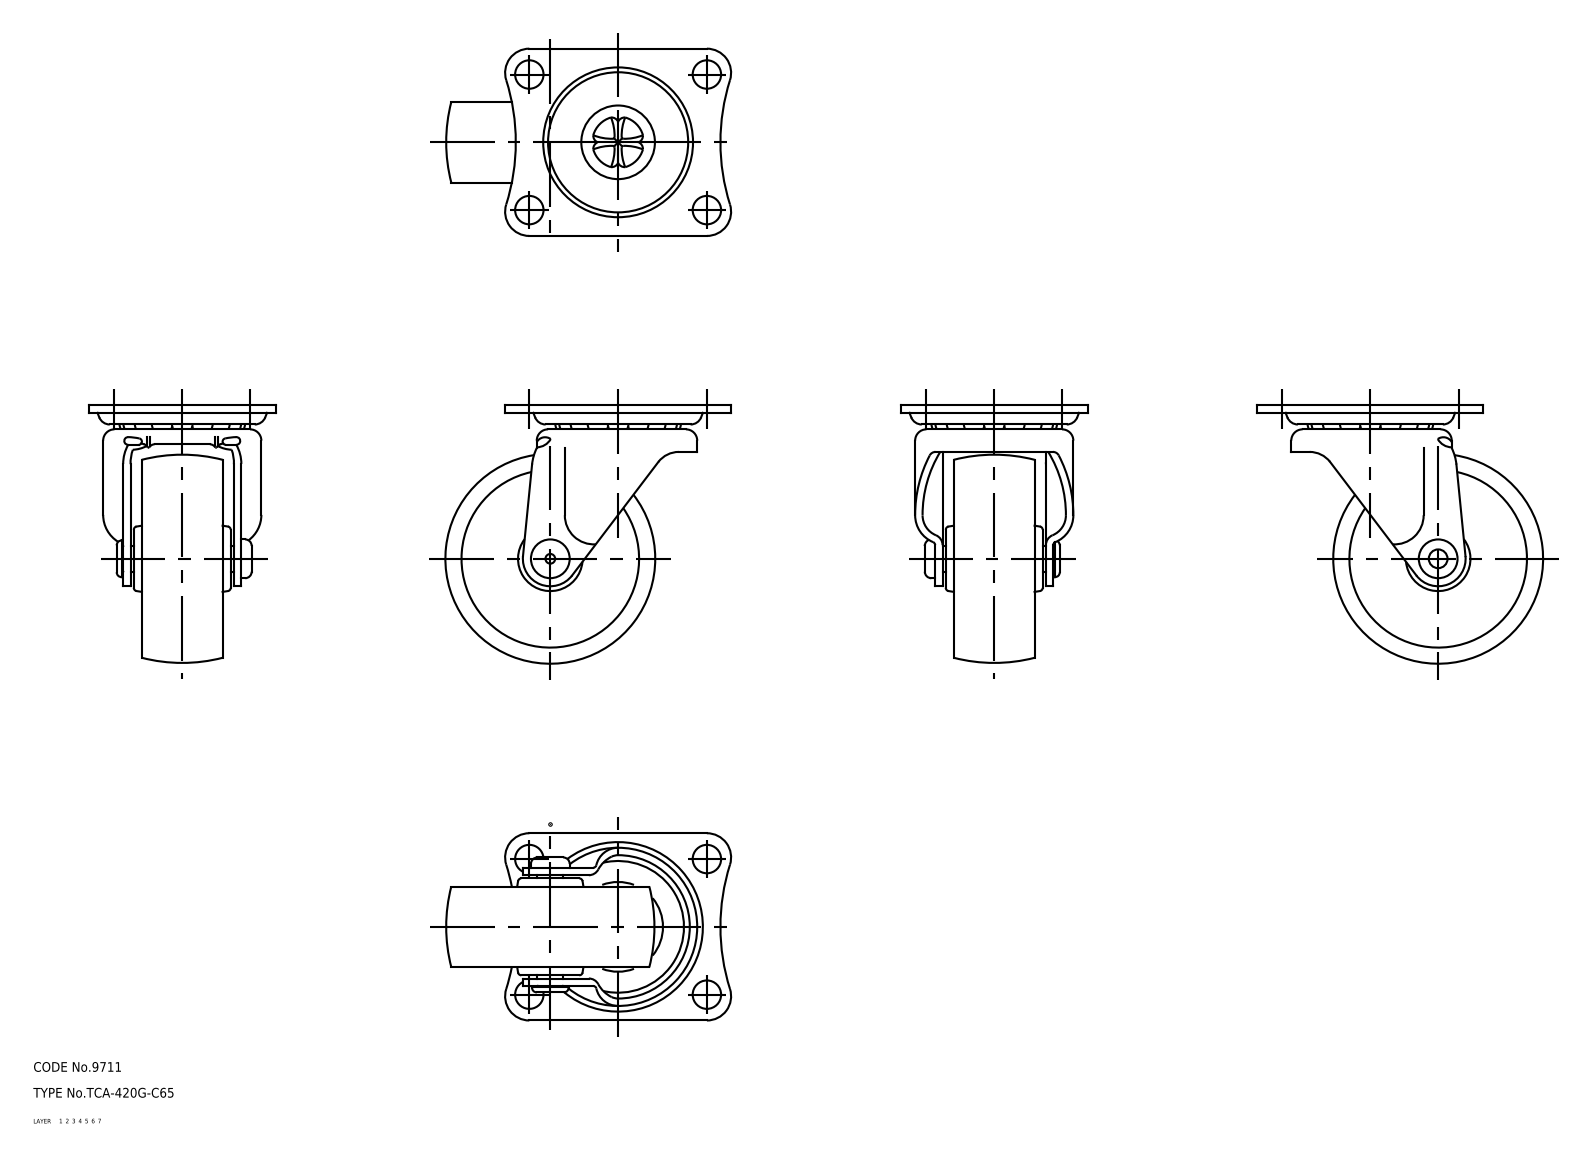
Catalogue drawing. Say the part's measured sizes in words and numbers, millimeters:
The part is named "wheel; mounting plate; main shaft; axle (+1 more)". Its 3-D file was written by "CADfix (AUTOMOTIVE_DESIGN)". It is 5 solids with 283 faces: 0 planar, 0 cylindrical and 283 other. Overall it measures 88.5 by 80 by 58 millimeters. Its volume is 86 770 cubic millimeters and its surface area 37 822 square millimeters.
